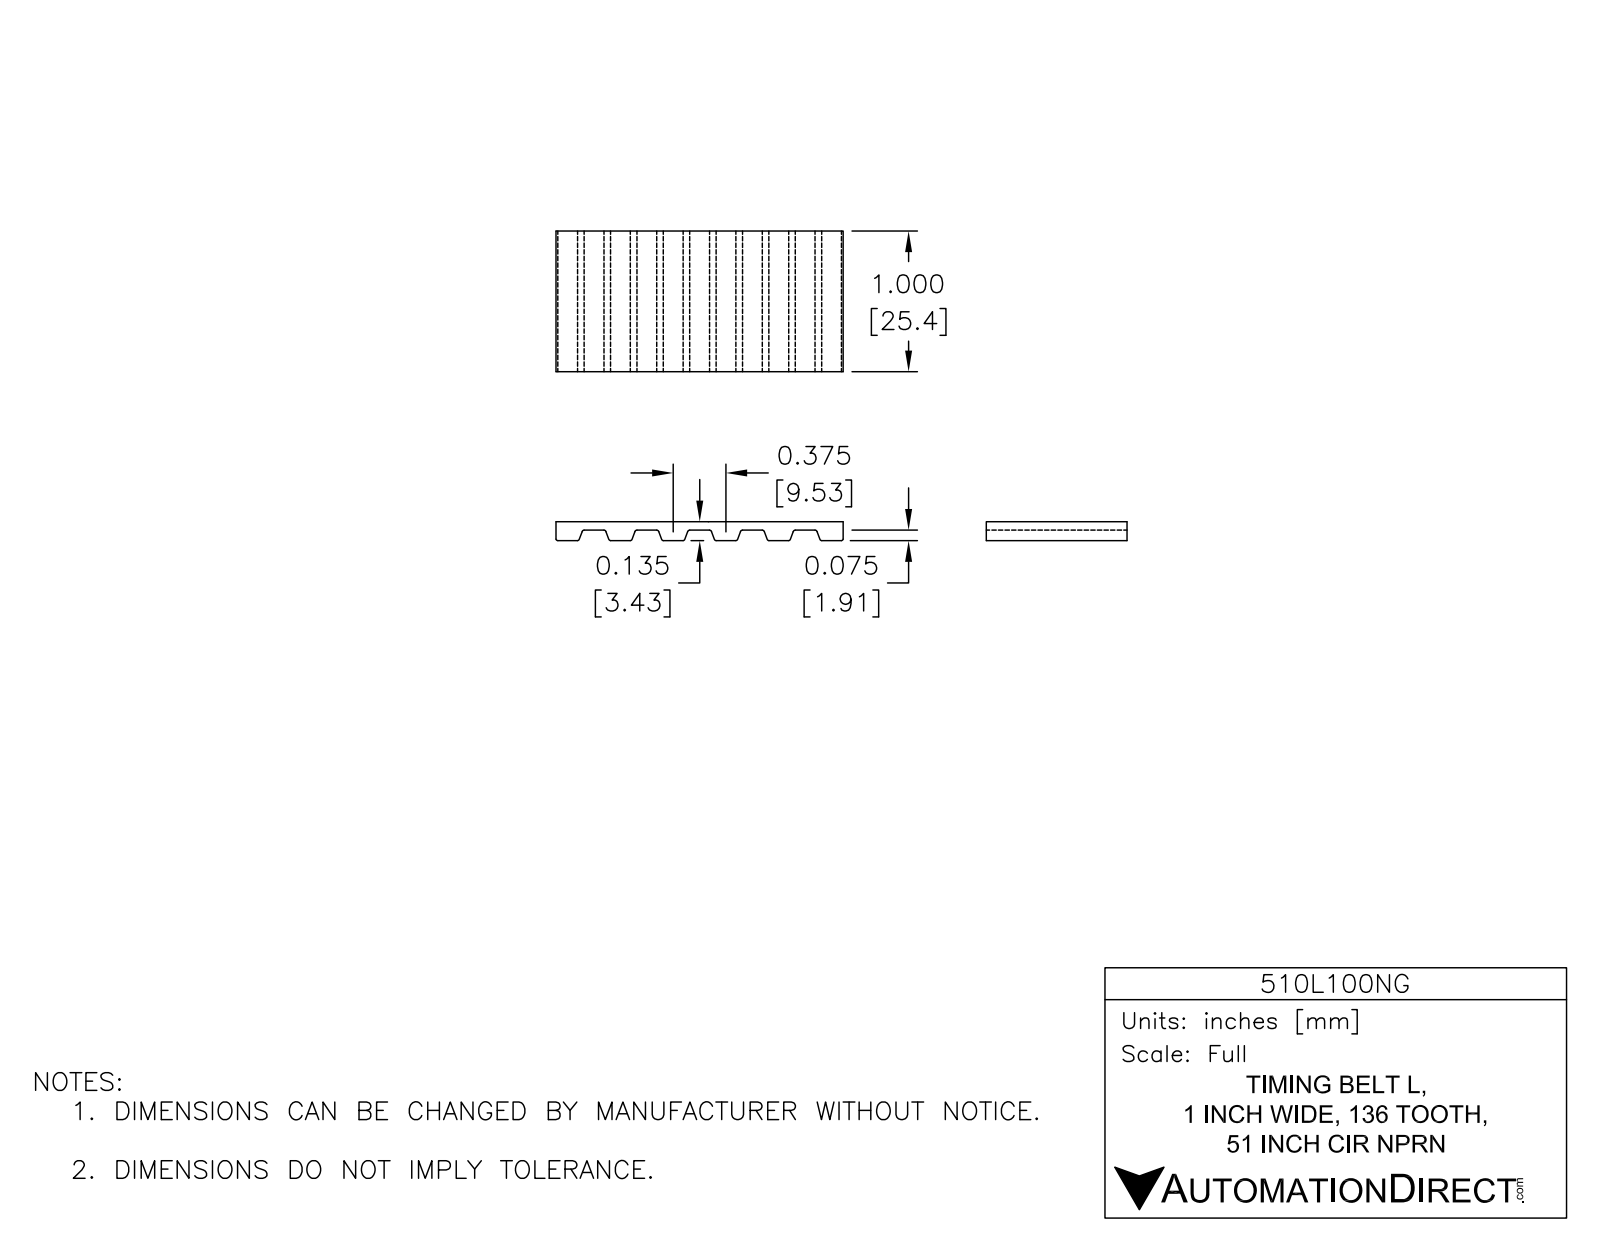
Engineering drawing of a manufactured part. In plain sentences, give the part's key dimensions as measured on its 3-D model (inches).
The part is named "510L100NG". Its 3-D file was written by "SolidWorks 2014 (AUTOMOTIVE_DESIGN)". It is 1 solid with 1104 faces: 521 planar, 583 cylindrical and 0 other. Overall it measures 23.788 by 3 by 1 inches. Its volume is 4.631 cubic inches and its surface area 123.1 square inches. Partial cylindrical surfaces (rounded edges, fillets, slot ends): 540 of radius 0.02, 2 of radius 1.435, 2 of radius 1.5. The main face-to-face distances are 0.065, 2.935, 3, 2.87, 0.14, 2.86, 0.075, 2.795, 1, 2.72.
